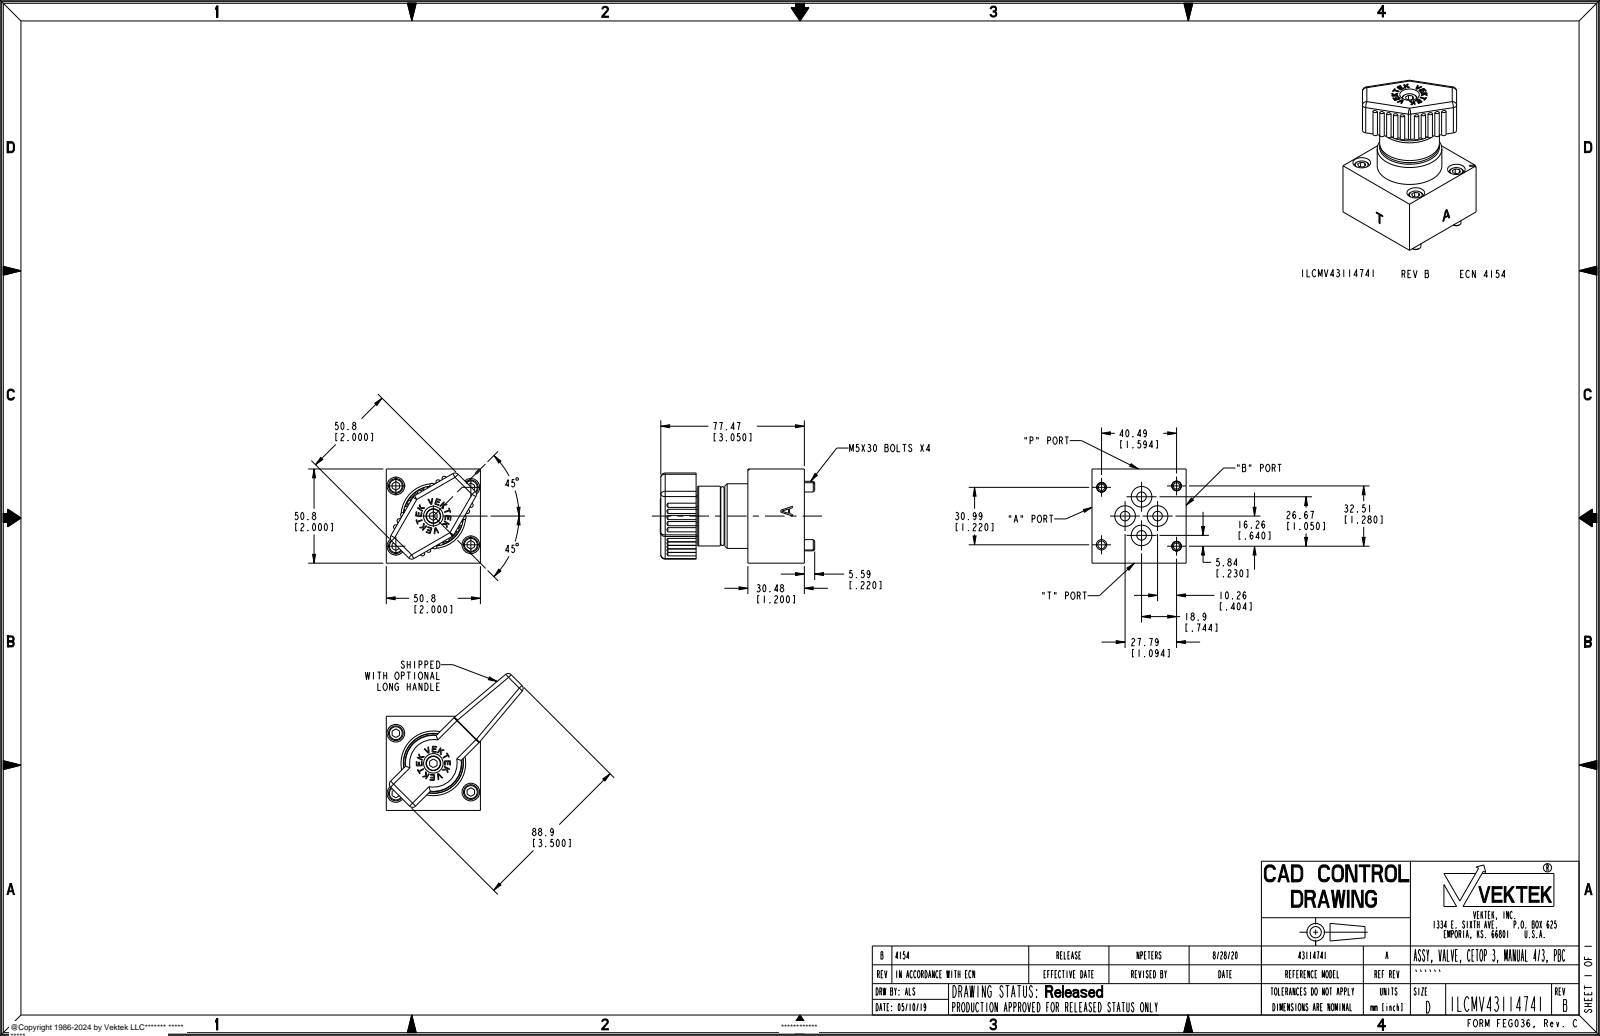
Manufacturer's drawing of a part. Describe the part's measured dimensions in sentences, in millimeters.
The part is named "ILCMV43114741_BASE; ILCMV43114741_ADAPTER; 85600903; 85600902 (+1 more)". Its 3-D file was written by "PRO/ENGINEER BY PARAMETRIC TECHNOLOGY CORPORATION, 2013320 (AP203_CONFIGURATION_CONTROLLED_3D_DESIGN_OF_MECHANICAL_PARTS_AND_ASSEMBLIES_MIM_LF)". It is 5 solids with 1642 faces: 1374 planar, 186 cylindrical and 82 other. Overall it measures 83.3 by 73.9 by 73.9 millimeters. Its volume is 137 100 cubic millimeters and its surface area 39 140 square millimeters. Round holes: 8 of diameter 5.2, 4 of diameter 9.5, 4 of diameter 11.1, 3 of diameter 5.1, 2 of diameter 5.1, 1 of diameter 5.2, 1 of diameter 5.2, 1 of diameter 10.5, 1 of diameter 12.7. Round bosses or shafts: 4 of diameter 8, 3 of diameter 5, 1 of diameter 34.9, 1 of diameter 32.3, 1 of diameter 7.9, 1 of diameter 5.6, 1 of diameter 4.8. Partial cylindrical surfaces (rounded edges, fillets, slot ends): 23 of radius 2.3, 20 of radius 1.2, 12 of radius 2.4, 10 of radius 0.8, 8 of radius 1.1, 8 of radius 1.6, 6 of radius 0.8, 4 of radius 3. The main face-to-face distances are 50.8, 30.5, 8.1, 27.9, 58.4, 2.5, 19.1, 36.1, 66.5, 10.8. The hole center spacings are 10.5, 11.1, 13.5, 13.7, 19.2, 19.8, 20, 22.2.
